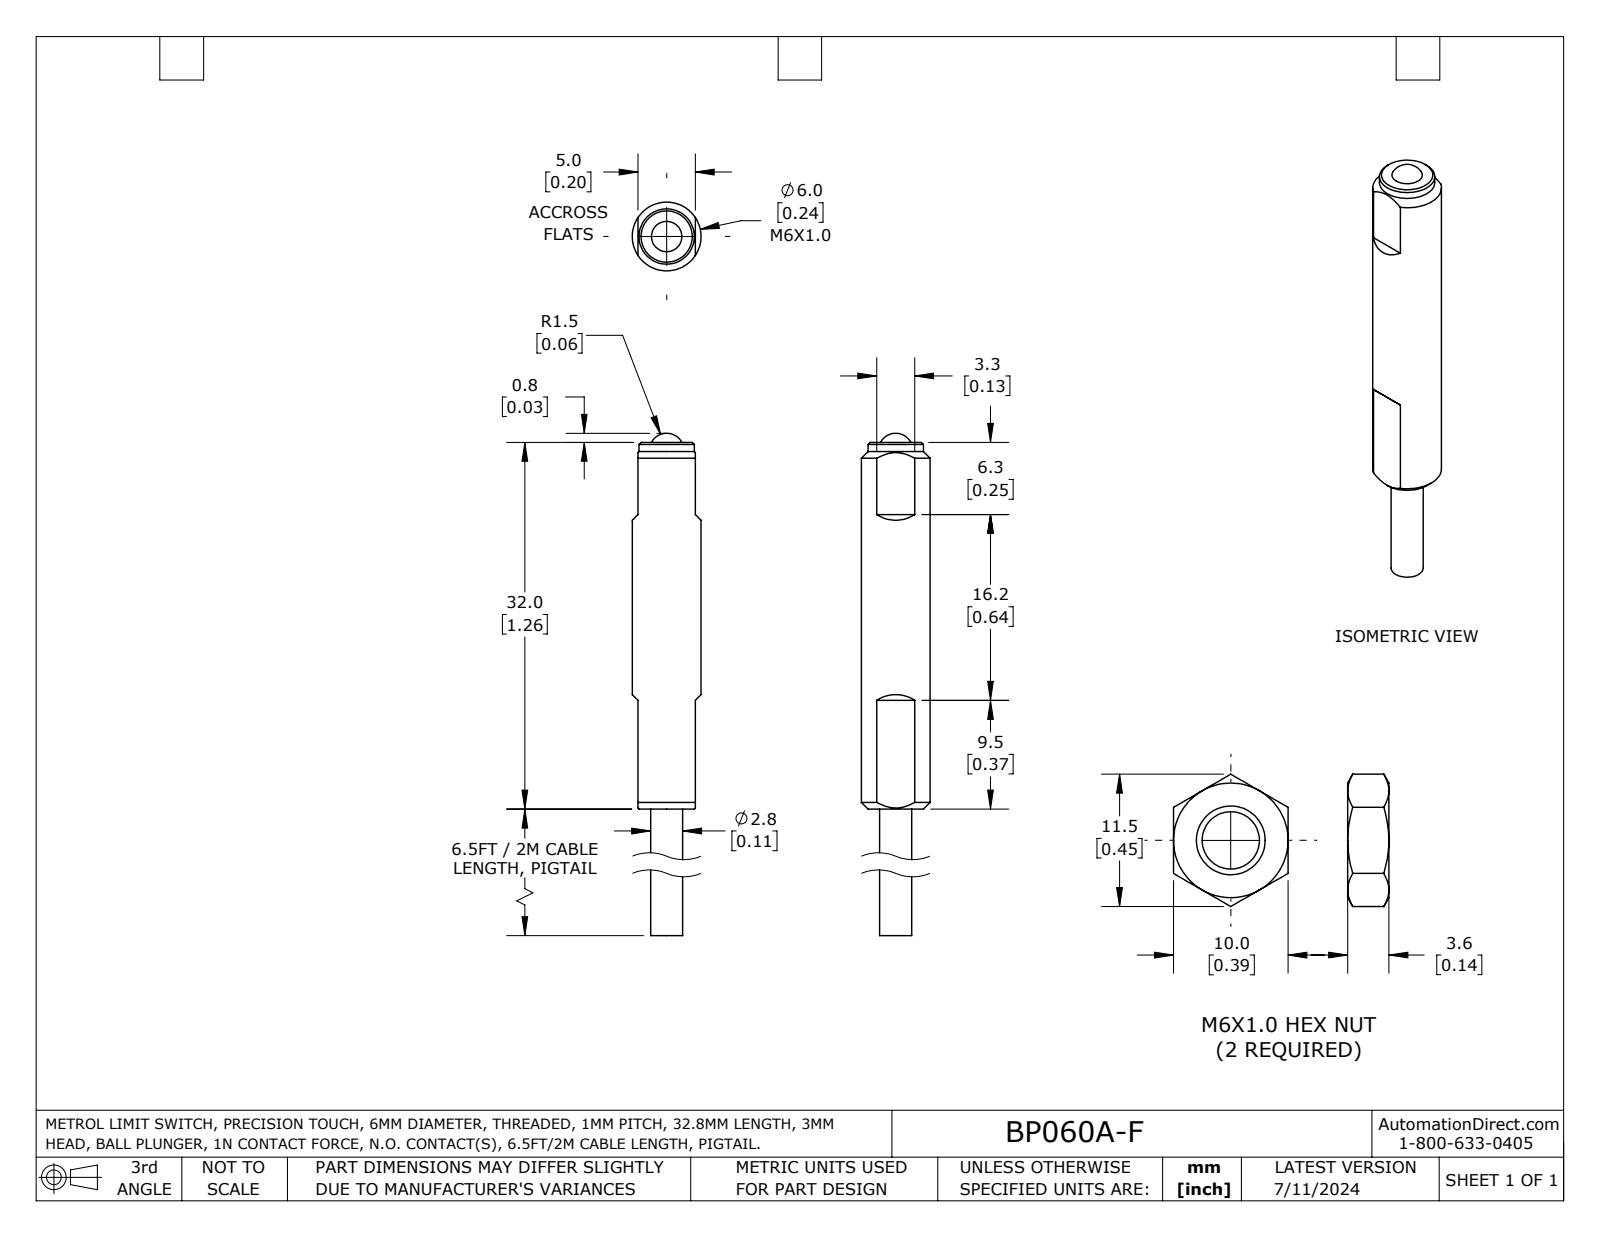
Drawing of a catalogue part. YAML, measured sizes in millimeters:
part_name: "BP060A-F"
step_written_by: "SolidWorks 2023 (AUTOMOTIVE_DESIGN)"
units: millimeters
bodies: {solids: 1, faces: 18, planar: 11, cylindrical: 3, other: 4}
overall_size: [42.8, 6, 6]
volume: 922
surface_area: 726
round_bosses_or_shafts:
  - {diameter: 6, count: 1}
  - {diameter: 4.83, count: 1}
  - {diameter: 2.8, count: 1}
face_to_face_distances: [5, 32, 10, 42, 15]
